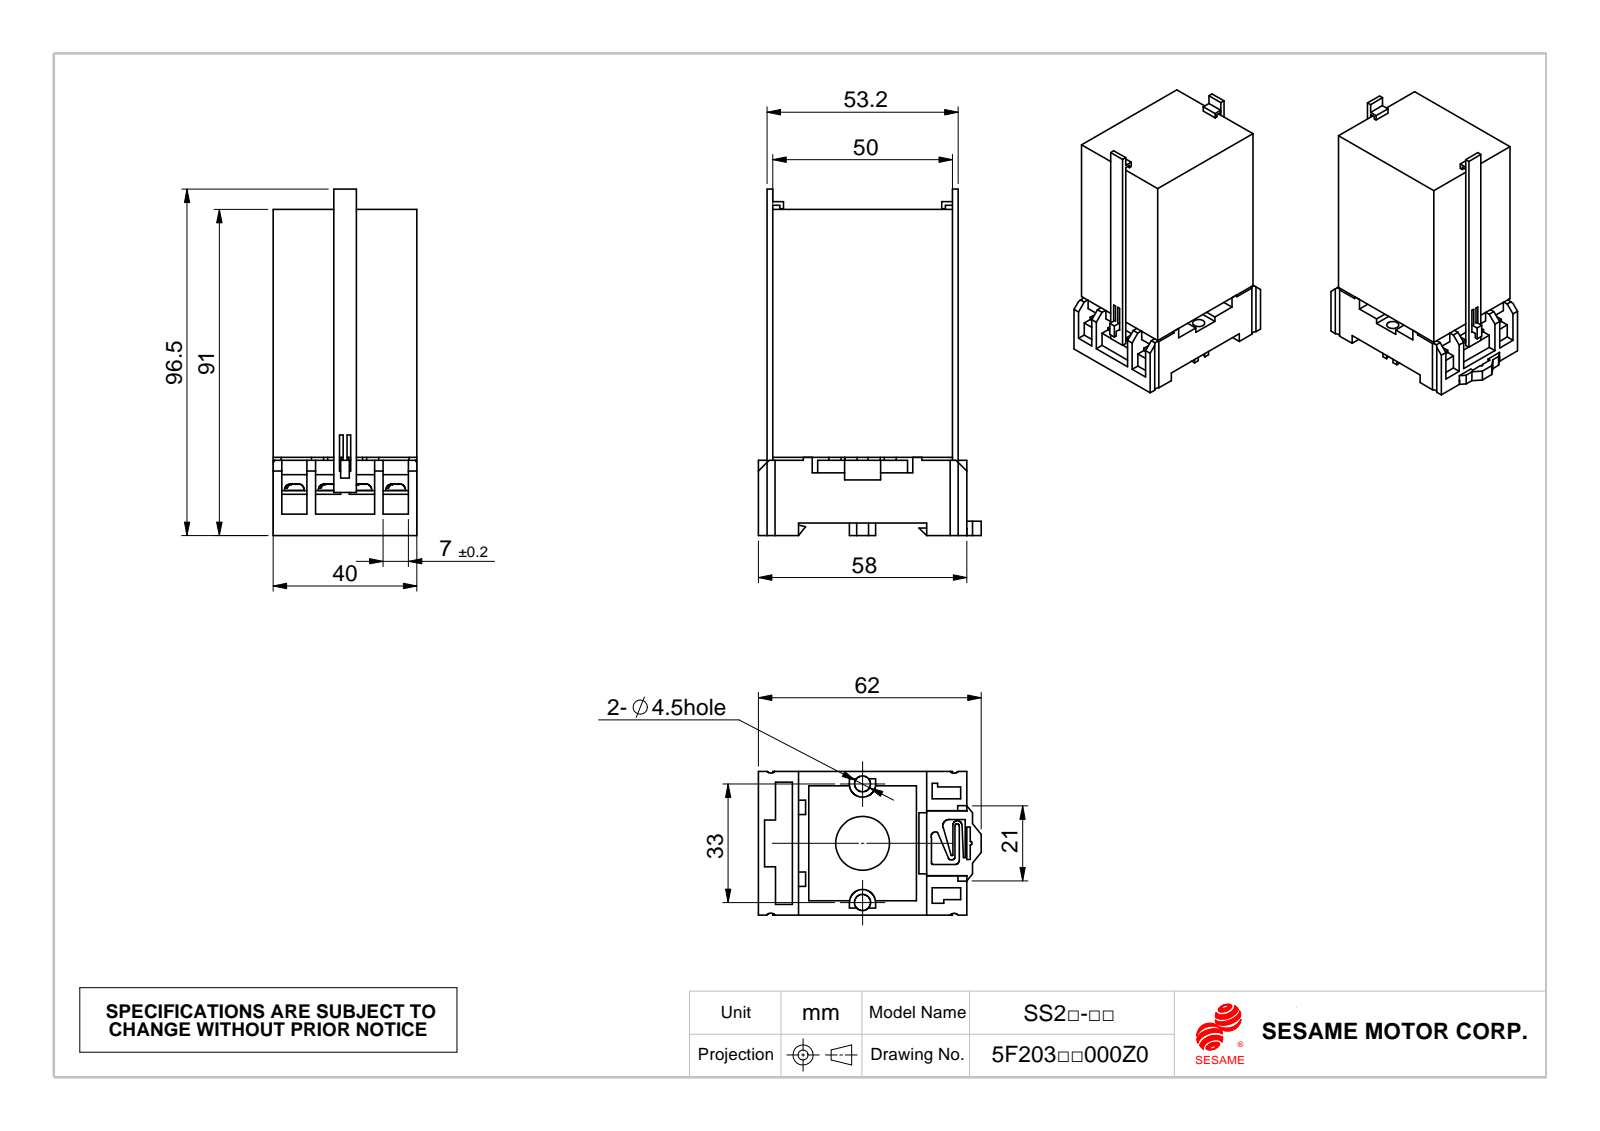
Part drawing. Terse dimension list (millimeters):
name: SS22_Default; 8-PIN_Default
written by: SolidWorks 2010 (CONFIG_CONTROL_DESIGN)
unit: mm
bodies: 20 solids, 675 faces (485 planar, 142 cylindrical, 48 other)
size: 96.5 × 62 × 40
volume: 172 955 mm³; area: 36 693 mm²
holes: 8× ⌀3, 8× ⌀6.4, 2× ⌀4.5
bosses: 8× ⌀5.5, 8× ⌀3.35, 1× ⌀15, 1× ⌀8
rounds: 32× R0.3, 4× R1.5, 2× R0.5, 2× R1, 2× R3.65, 1× R0.29, 1× R0.61, 1× R0.98
face distances: 40, 50, 69, 2.4, 9.4, 18.8, 1, 9.5, 5, 4
hole spacings: 9.4, 39.92, 18.8, 19.55, 22.71, 28.74, 36.23, 38.8
